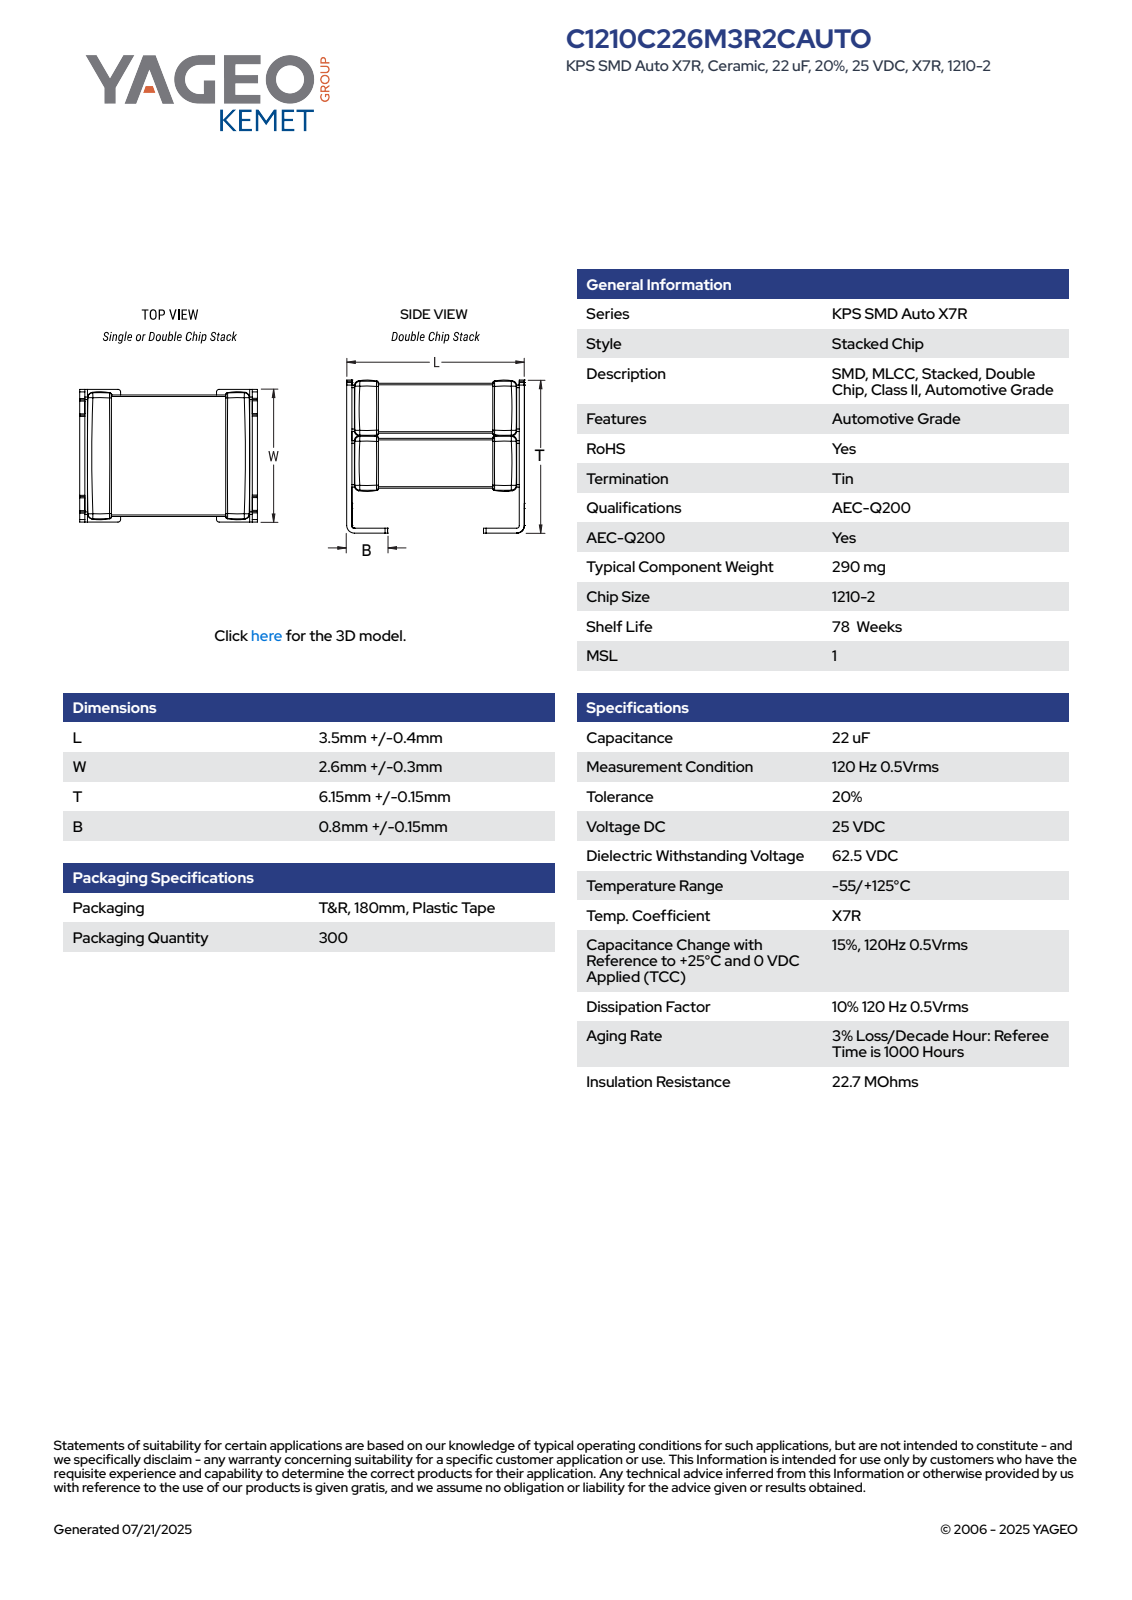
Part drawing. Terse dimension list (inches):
name: CCSS_S2_1210-2_L3.9W2.9T6.3B0.95
written by: SolidWorks 2014 (AUTOMOTIVE_DESIGN)
unit: in
bodies: 4 solids, 113 faces (109 planar, 4 cylindrical, 0 other)
size: 0.248 × 0.154 × 0.114
volume: 0.003 in³; area: 0.211 in²
face distances: 0.154, 0.15, 0.112, 0.077, 0.156, 0.079, 0.081, 0.075, 0.167, 0.114
